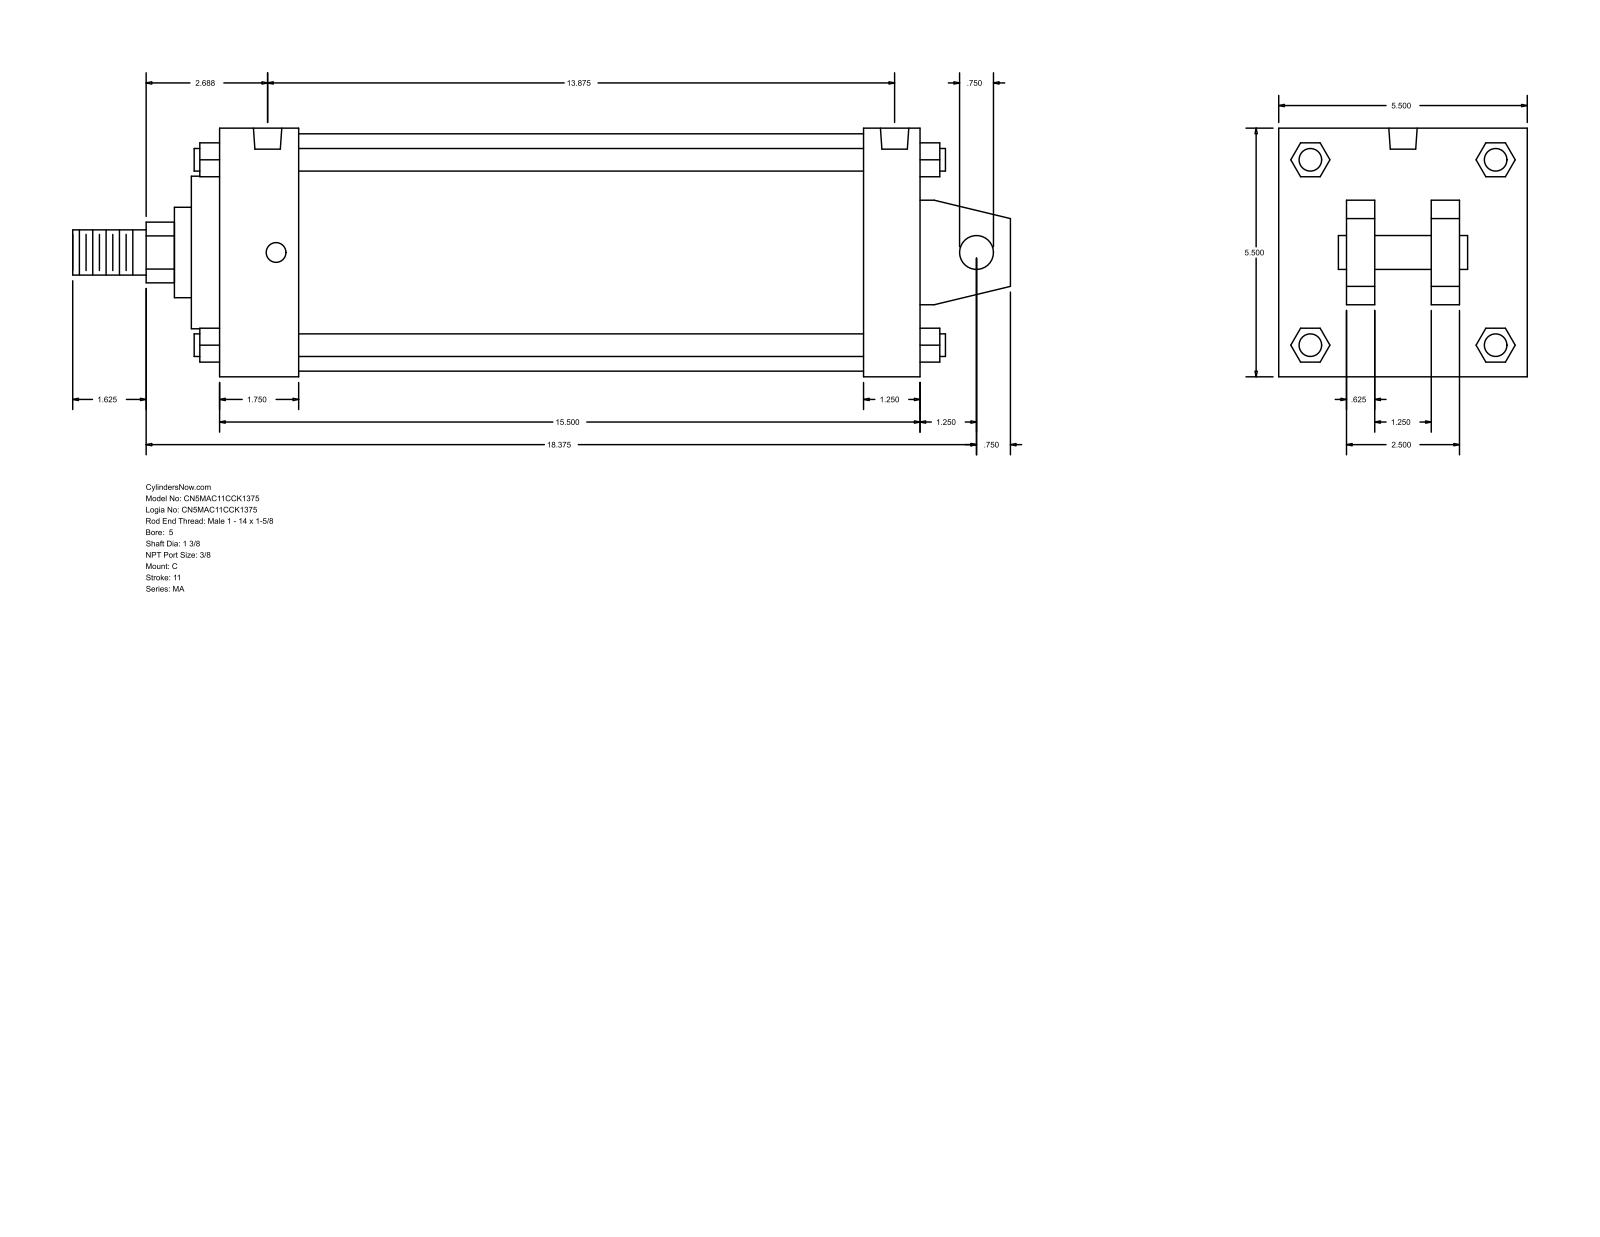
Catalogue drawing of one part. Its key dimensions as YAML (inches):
part_name: "MA_C__0500_1.375"
step_written_by: "GSSL Pune (CONFIG_CONTROL_DESIGN)"
units: inches
bodies: {solids: 0, faces: 141, planar: 109, cylindrical: 32, other: 0}
overall_size: [20.75, 5.5, 5.5]
round_holes:
  - {diameter: 0.437, count: 4}
  - {diameter: 0.627, count: 2}
round_bosses_or_shafts:
  - {diameter: 0.5, count: 4}
  - {diameter: 5.25, count: 1}
  - {diameter: 3.375, count: 1}
  - {diameter: 2, count: 1}
  - {diameter: 1.375, count: 1}
  - {diameter: 1, count: 1}
  - {diameter: 0.75, count: 1}
partial_cylinders:
  - {radius: 0.672, count: 1}
face_to_face_distances: [5.5, 15.5, 0.625, 14.25, 1.25, 1.75, 12.5, 13.75, 2.125, 1.5]
hole_center_spacings: [13.5, 0.187, 0.188, 13.687, 13.688, 13.875]
